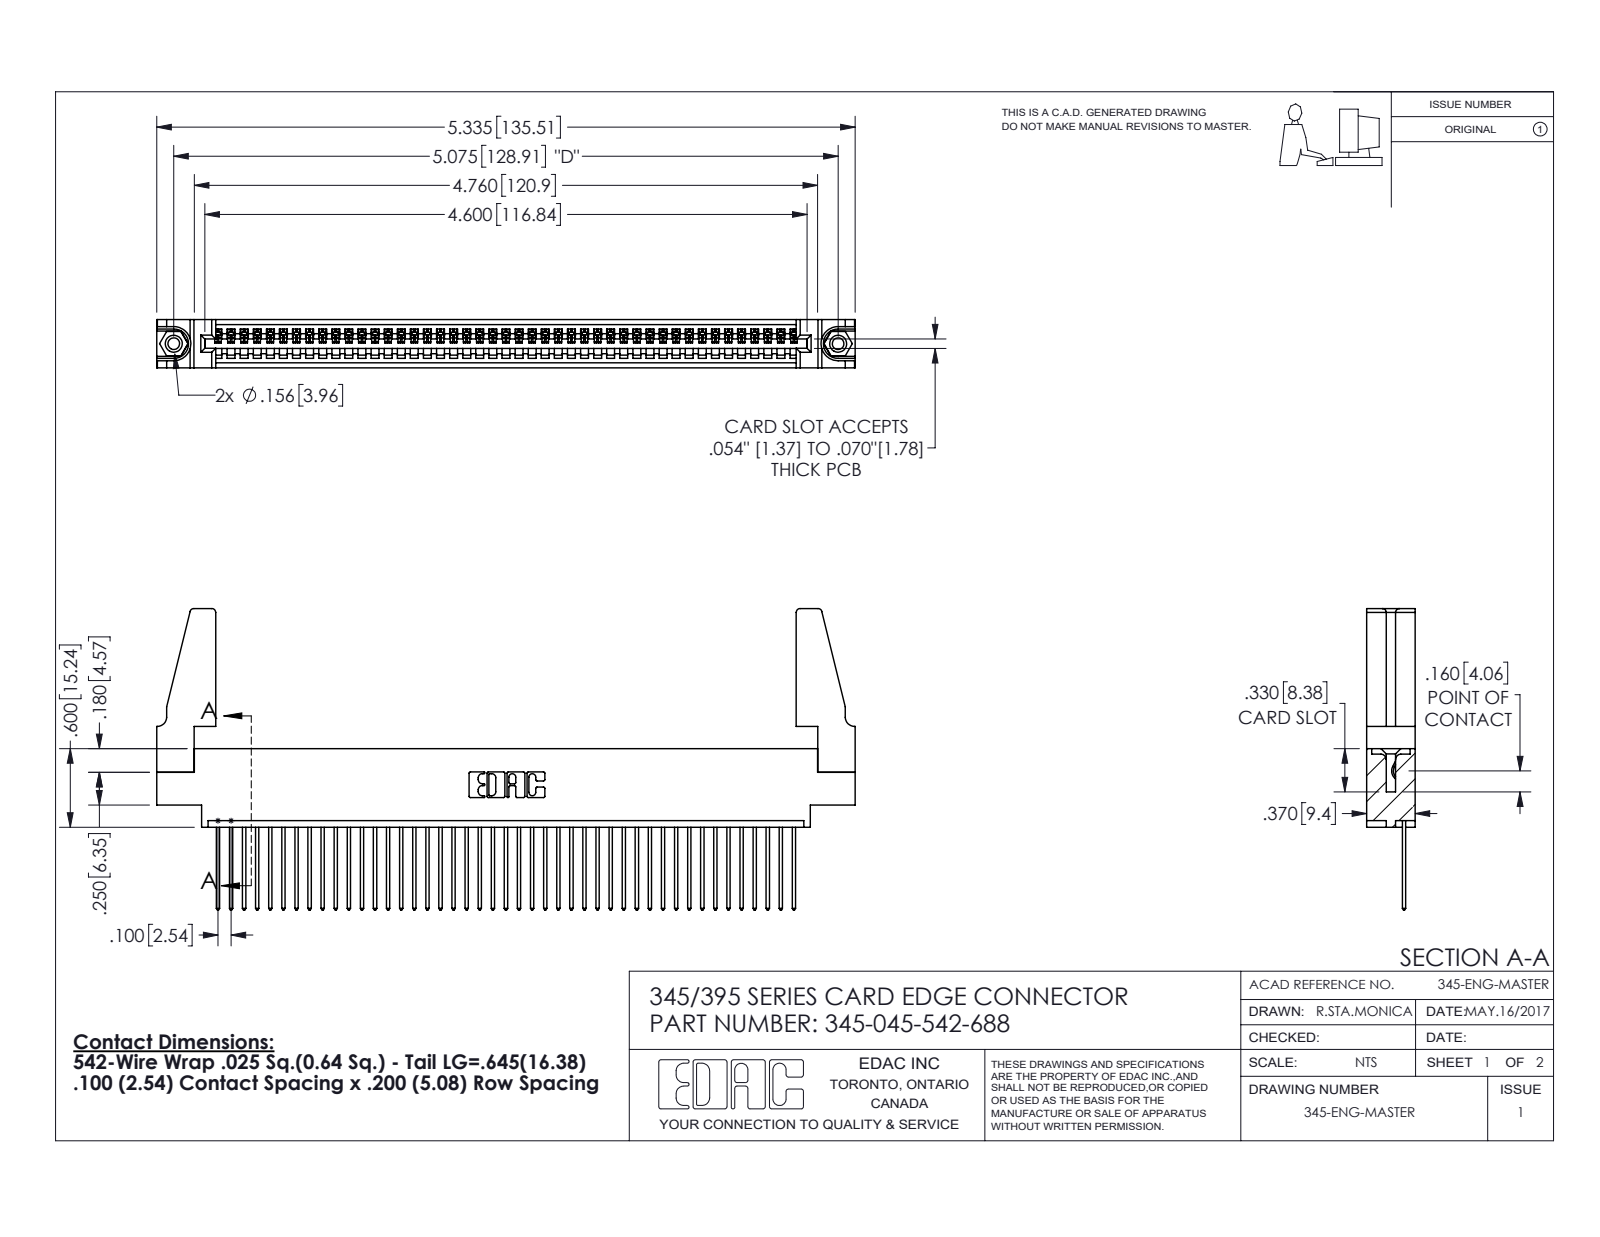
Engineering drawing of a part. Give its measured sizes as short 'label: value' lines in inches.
name: 345-045-542-688; 345-292-001_345-293-142; 345-220-078_345-220-088; 345 Part_0.170 Offset - 0.156 Dia-TH (+1 more)
written by: SolidWorks 2016 (CONFIG_CONTROL_DESIGN)
unit: in
bodies: 50 solids, 2864 faces (1956 planar, 892 cylindrical, 16 other)
size: 5.336 × 2.302 × 0.37
volume: 0.985 in³; area: 32.63 in²
holes: 2× ⌀0.089, 2× ⌀0.125, 2× ⌀0.156, 1× ⌀0.064
bosses: 2× ⌀0.155
rounds: 90× R0.006, 90× R0.01, 22× R0.01, 8× R0.03, 6× R0.007, 6× R0.031, 3× R0.026, 2× R0.031
face distances: 0.072, 0.298, 0.37, 0.098, 0.272, 0.025, 0.2, 0.225, 0.175, 0.149
hole spacings: 0.27, 4.839, 5.075
